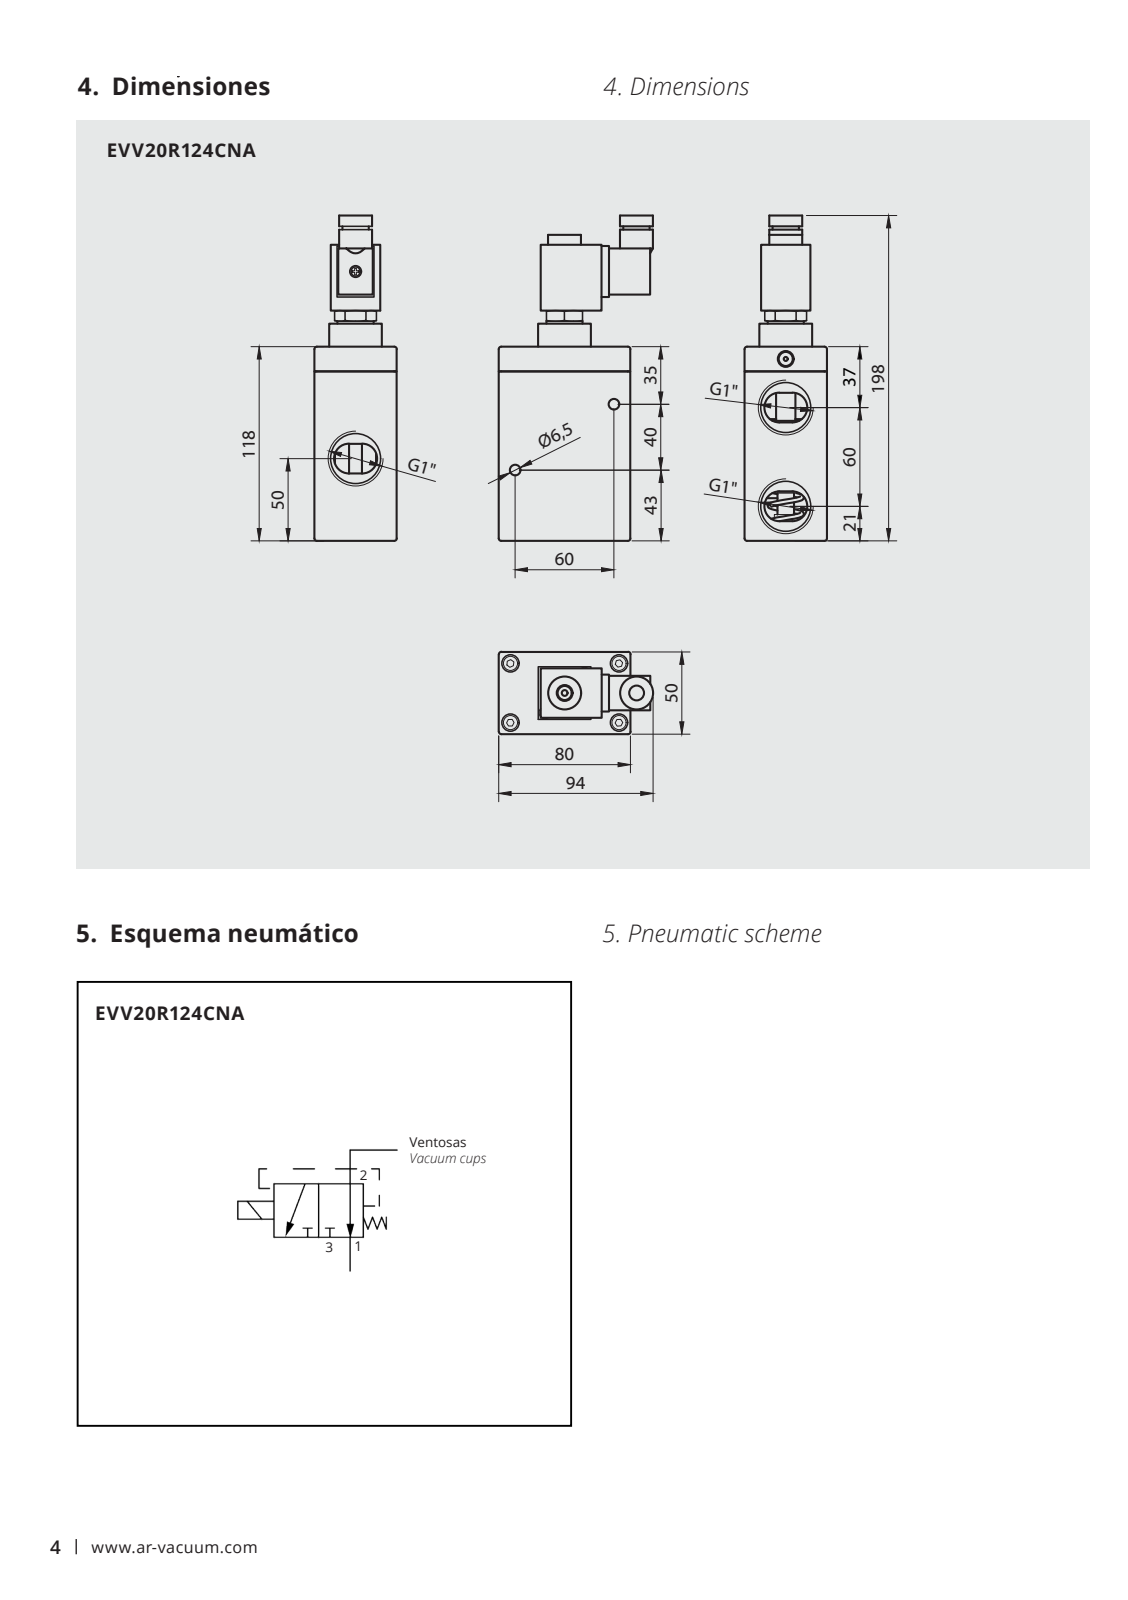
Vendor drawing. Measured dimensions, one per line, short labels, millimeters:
name: Pieza49
written by: Autodesk Inventor 2024 (AUTOMOTIVE_DESIGN)
unit: mm
bodies: 1 solid, 225 faces (137 planar, 54 cylindrical, 34 other)
size: 197.7 × 93.7 × 50
volume: 535 153 mm³; area: 60 513 mm²
holes: 4× ⌀10.5, 3× ⌀30.29, 2× ⌀2.5, 2× ⌀4.3, 2× ⌀6.2, 2× ⌀6.5, 2× ⌀8.57, 1× ⌀1.5, 1× ⌀3.2, 1× ⌀7, 1× ⌀9, 1× ⌀10.1
bosses: 2× ⌀20, 2× ⌀6, 2× ⌀4, 1× ⌀37.5, 1× ⌀22, 1× ⌀16, 1× ⌀5.6, 1× ⌀3
rounds: 12× R1.5, 1× R1.75
face distances: 50, 40, 80, 10, 25.5, 118, 6.5, 56, 4.5, 30
hole spacings: 34.56, 37.59, 40.7, 3.5, 14.71, 16.97, 18.44, 19.6
